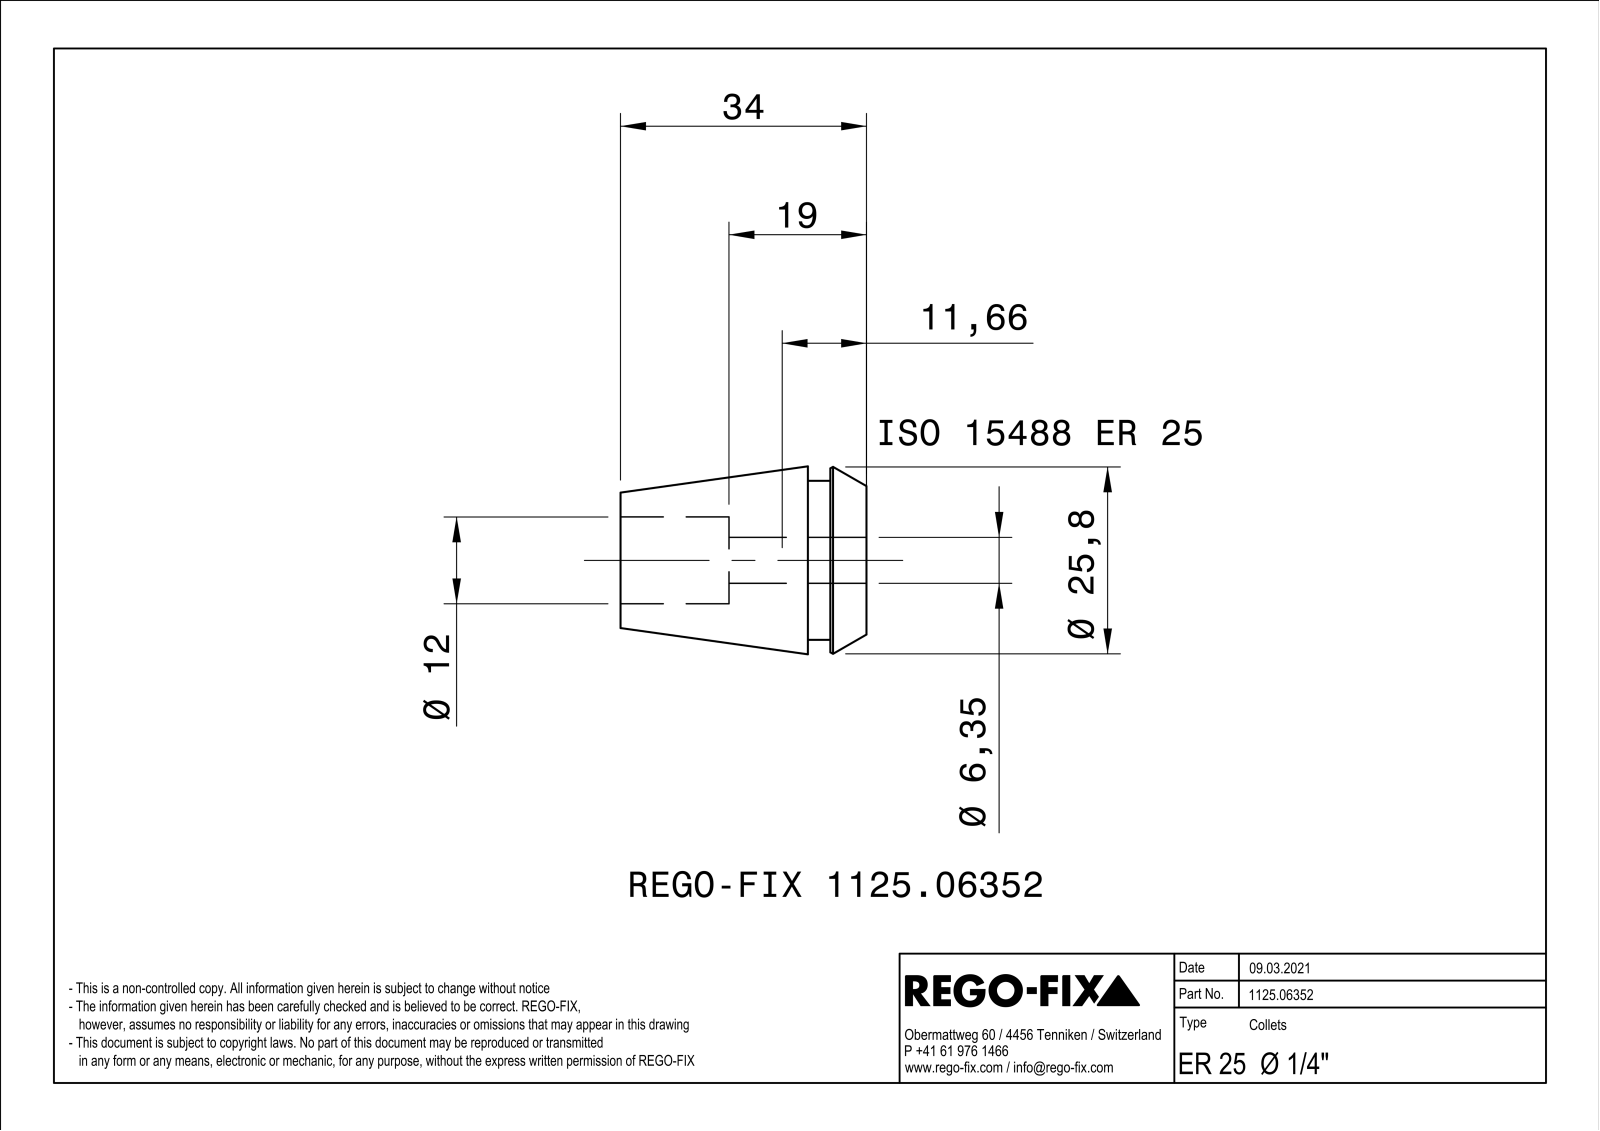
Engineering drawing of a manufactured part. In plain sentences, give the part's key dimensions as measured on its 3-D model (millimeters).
The part is named "NOCUT". Its 3-D file was written by "SIEMENS PLM Software Solid Edge ST10 (AUTOMOTIVE_DESIGN)". It is 1 solid with 256 faces: 88 planar, 48 cylindrical and 120 other. Overall it measures 34 by 25.99 by 25.99 millimeters. Its volume is 9 128 cubic millimeters and its surface area 8 911 square millimeters. Round holes: 1 of diameter 12. Round bosses or shafts: 1 of diameter 22. Partial cylindrical surfaces (rounded edges, fillets, slot ends): 12 of radius 0.4, 1 of radius 3.17. The main face-to-face distances are 0.8, 0.82, 0.78, 8.1, 34, 25.9, 5, 3.1, 29, 19.
